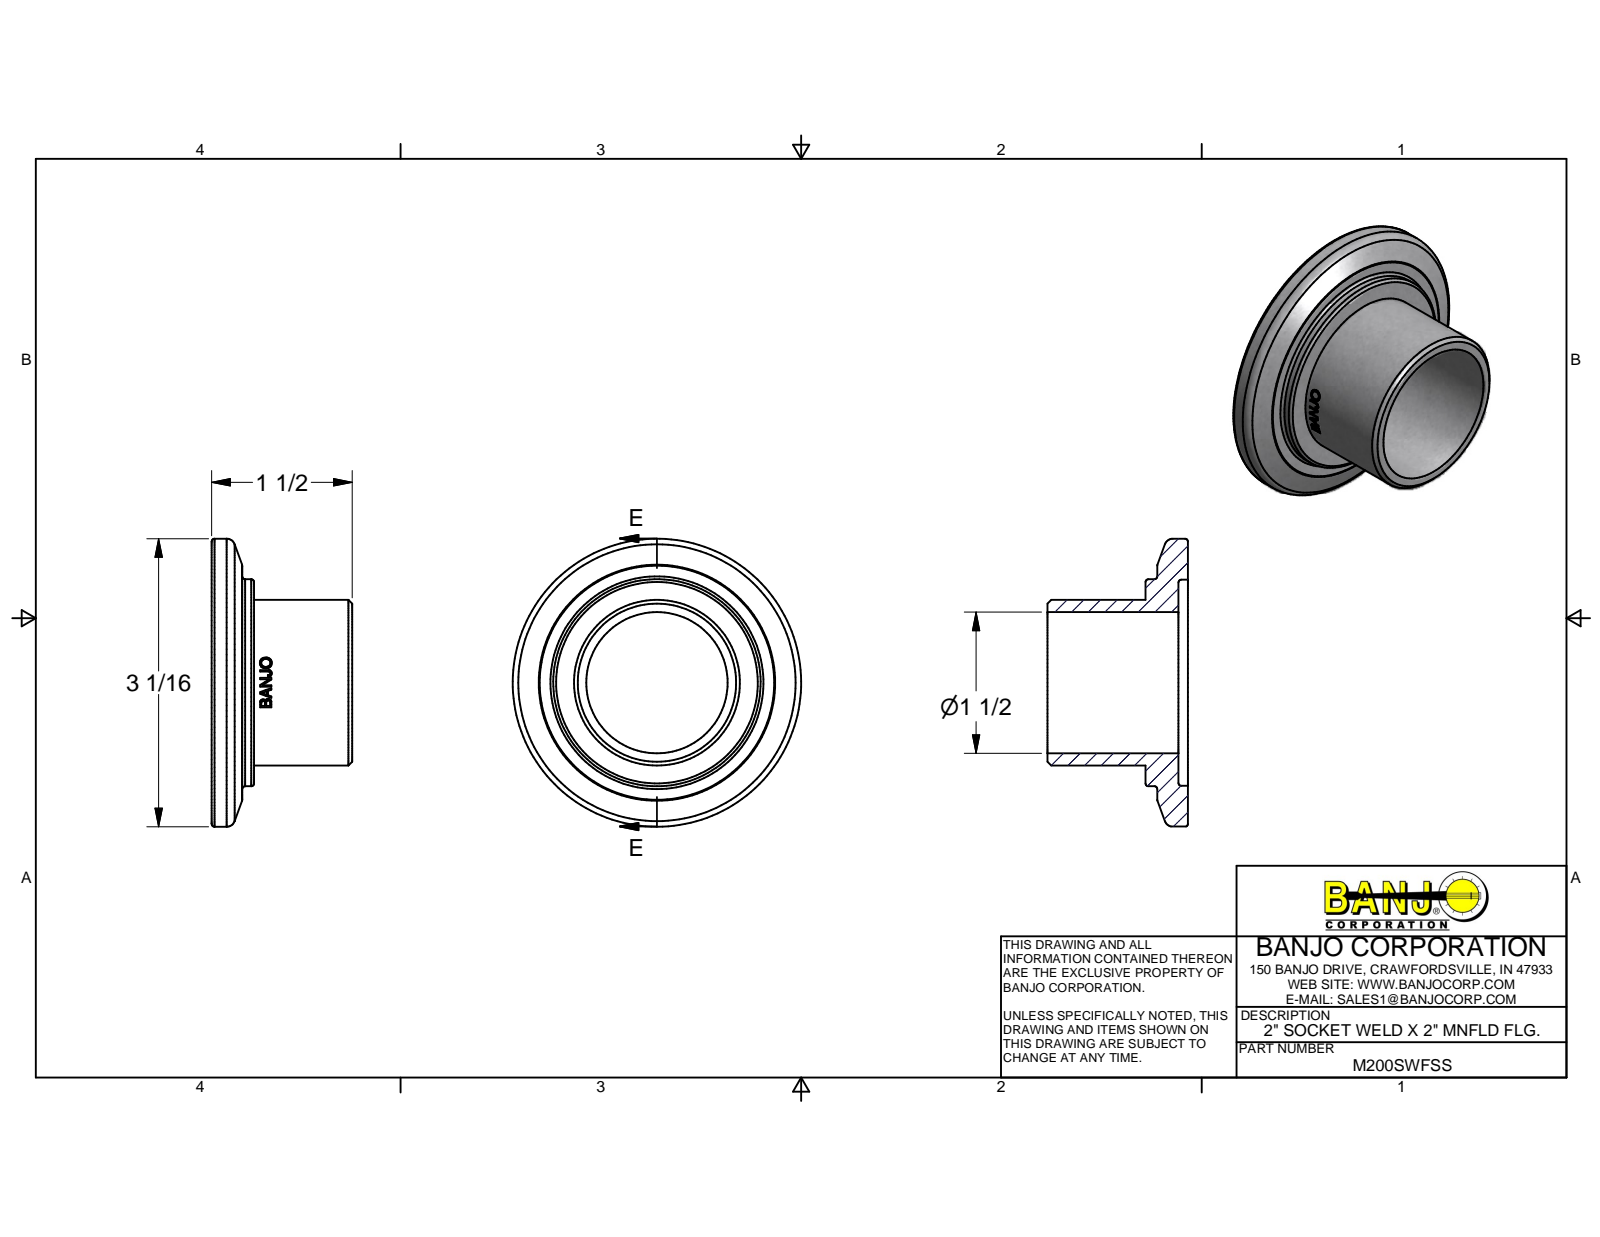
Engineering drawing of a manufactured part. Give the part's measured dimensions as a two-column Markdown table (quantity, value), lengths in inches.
| quantity | value |
| --- | --- |
| part name | M200SWFSS |
| STEP written by | Autodesk Inventor 2014 (AUTOMOTIVE_DESIGN) |
| units | inches |
| bodies | 1 solid, 241 faces (95 planar, 25 cylindrical, 121 other) |
| overall size | 3.06 × 3.06 × 1.49 |
| volume | 2.415 in³ |
| surface area | 26.92 in² |
| round holes (diameter × count) | 1.5 × 1, 2.19 × 1 |
| round bosses / shafts (diameter × count) | 3.06 × 1, 2.2 × 1, 1.76 × 1 |
| partial cylindrical surfaces (radius × count) | 0.85 × 1 |
| main face-to-face distances | 0.1, 0.349, 0.449, 0.125, 0.224, 0.324, 1.041, 1.166, 1.39, 1.49 |
